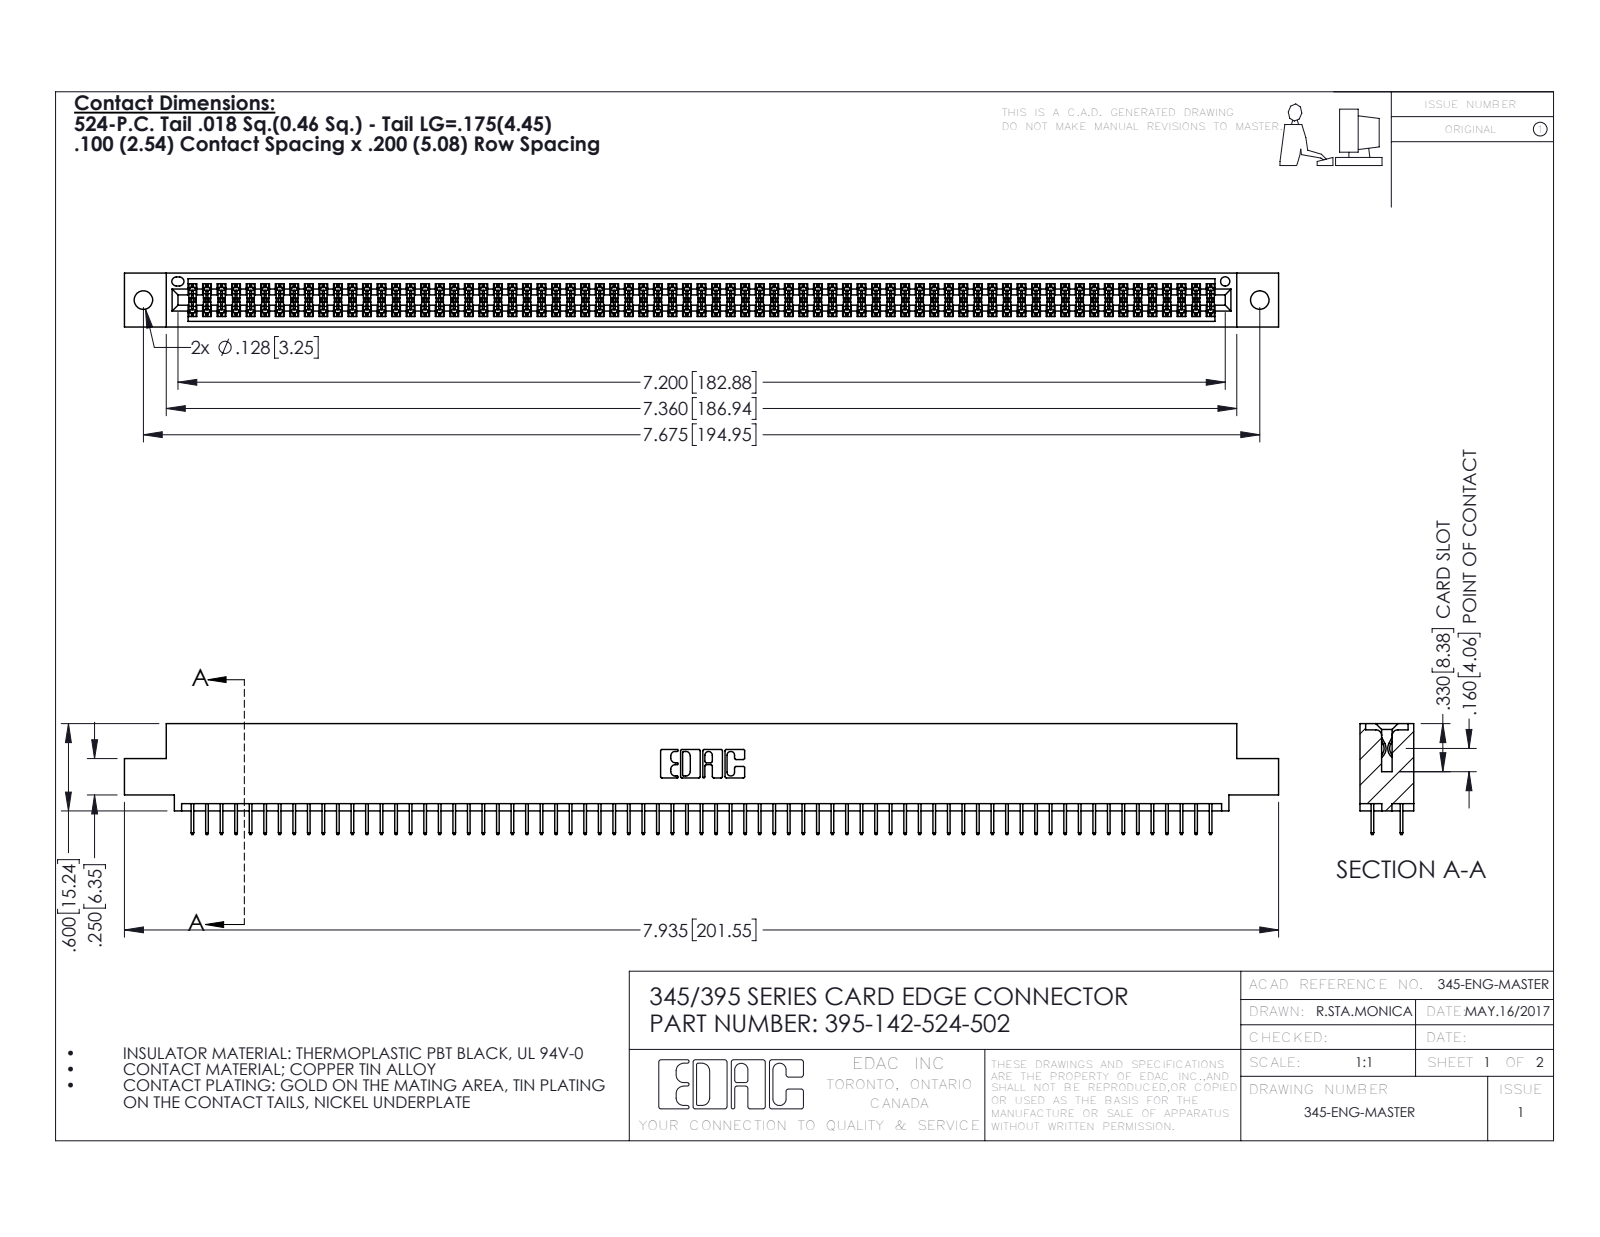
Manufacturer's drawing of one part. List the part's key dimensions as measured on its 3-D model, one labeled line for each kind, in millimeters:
Part name (STEP PRODUCT): 345-292-001_345-293-124; 345 Part_0.110 Offset - 0.128 Dia; 395-142-524-502
STEP written by: SolidWorks 2016 (CONFIG_CONTROL_DESIGN)
Units: millimetres
Bodies: 143 solids, 7798 faces (5622 planar, 2176 cylindrical, 0 other)
Overall size (bounding box): 201.5 × 19.4 × 9.4
Volume: 19 520 mm³ · Surface area: 28 670 mm²
Round holes (diameter × count): ⌀3.3 ×2, ⌀1.6 ×1
Partial cylindrical surfaces — rounded edges, fillets, slot ends (radius × count): R0.2 ×213, R0.3 ×22, R0.2 ×6, R0.8 ×6, R0.7 ×3, R0.4 ×2, R0.5 ×2, R0.6 ×2
Main face-to-face distances: 1.8, 7.6, 5.1, 9.4, 2.5, 6.9, 0.6, 5.7, 1.8, 4.4
Hole centre spacings: 6.9, 189, 194.9
